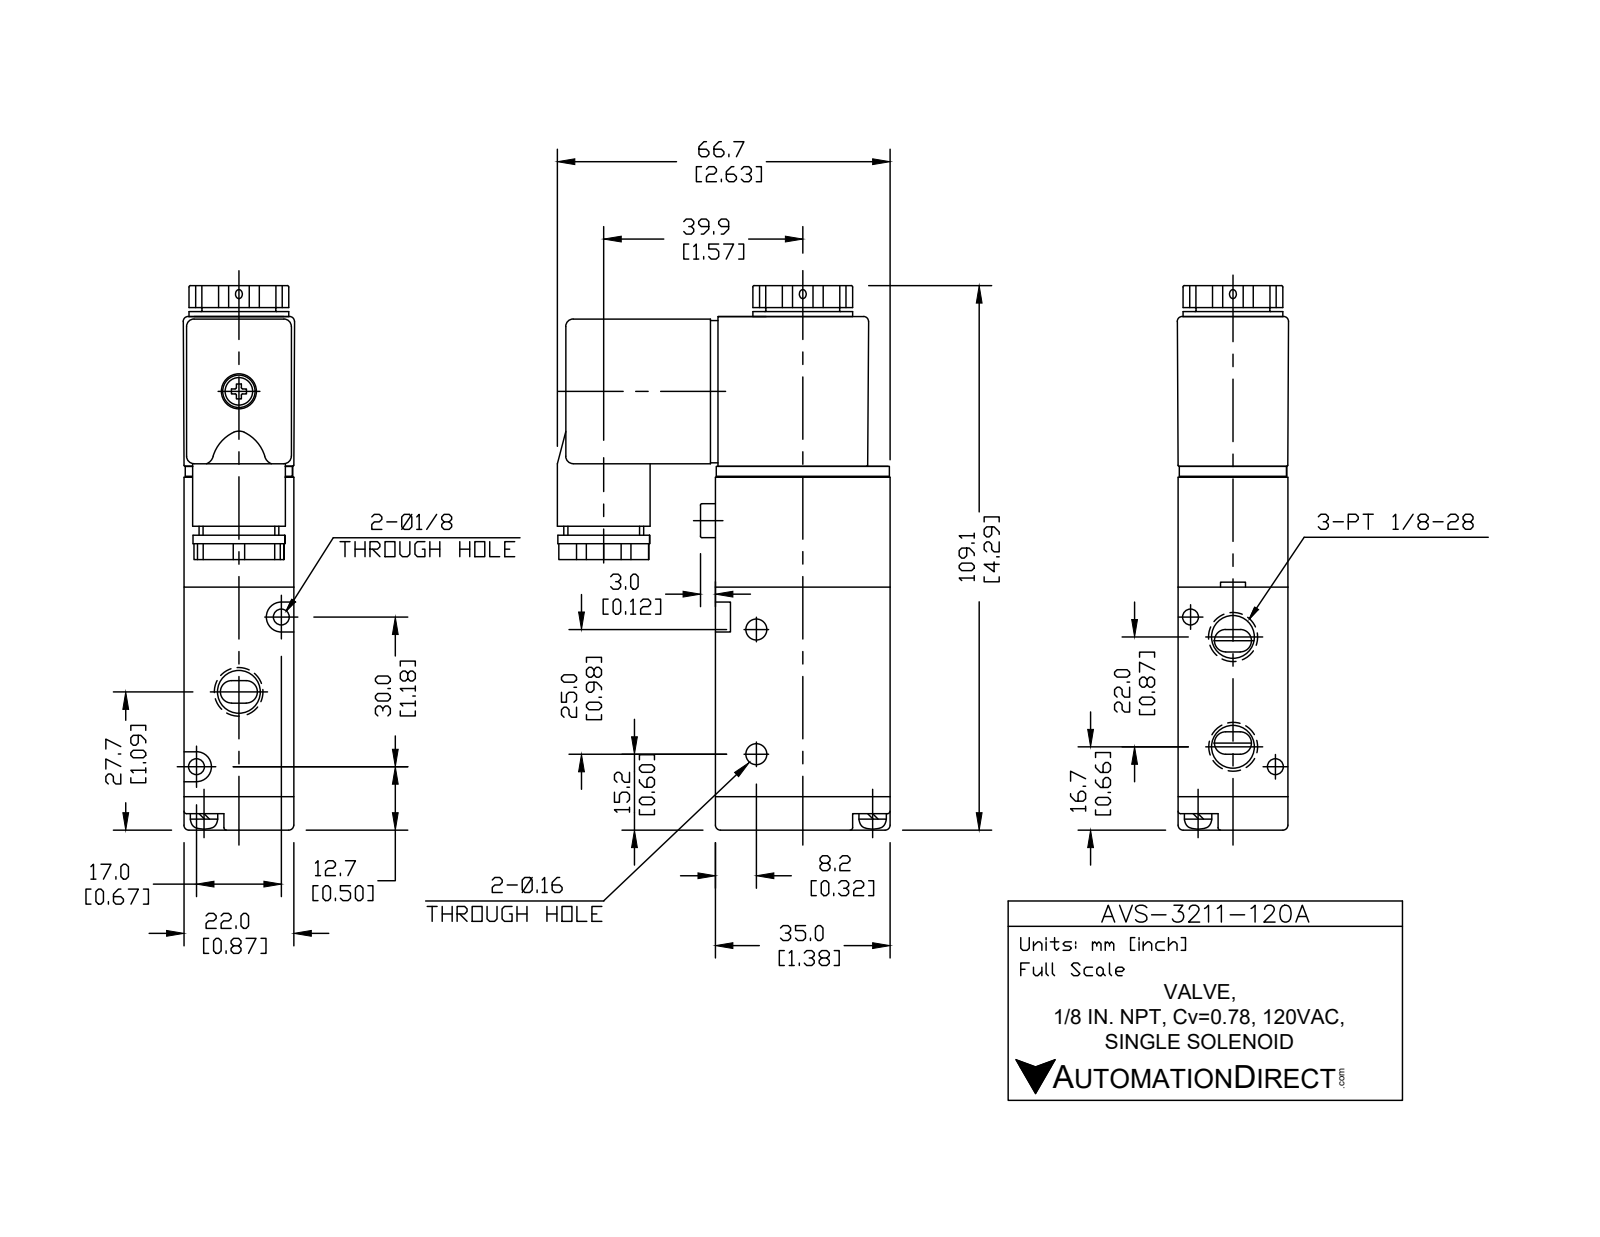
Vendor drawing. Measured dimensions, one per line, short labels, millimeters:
name: AVS-3211-120A
written by: SolidWorks 2015 (CONFIG_CONTROL_DESIGN)
unit: mm
bodies: 4 solids, 159 faces (84 planar, 53 cylindrical, 22 other)
size: 109.1 × 66.7 × 22
volume: 96 545 mm³; area: 23 276 mm²
holes: 3× ⌀8.43, 2× ⌀3.3, 2× ⌀4.3, 1× ⌀9.3
bosses: 1× ⌀20, 1× ⌀18.6, 1× ⌀18.4, 1× ⌀16, 1× ⌀14.8, 1× ⌀6.8
rounds: 11× R0.5, 10× R1, 2× R3
face distances: 0.5, 21.5, 42, 22, 6.7, 48.7, 21, 102.4, 35, 30
hole spacings: 9.39, 11, 17.24, 27.35, 22, 25, 34.48
